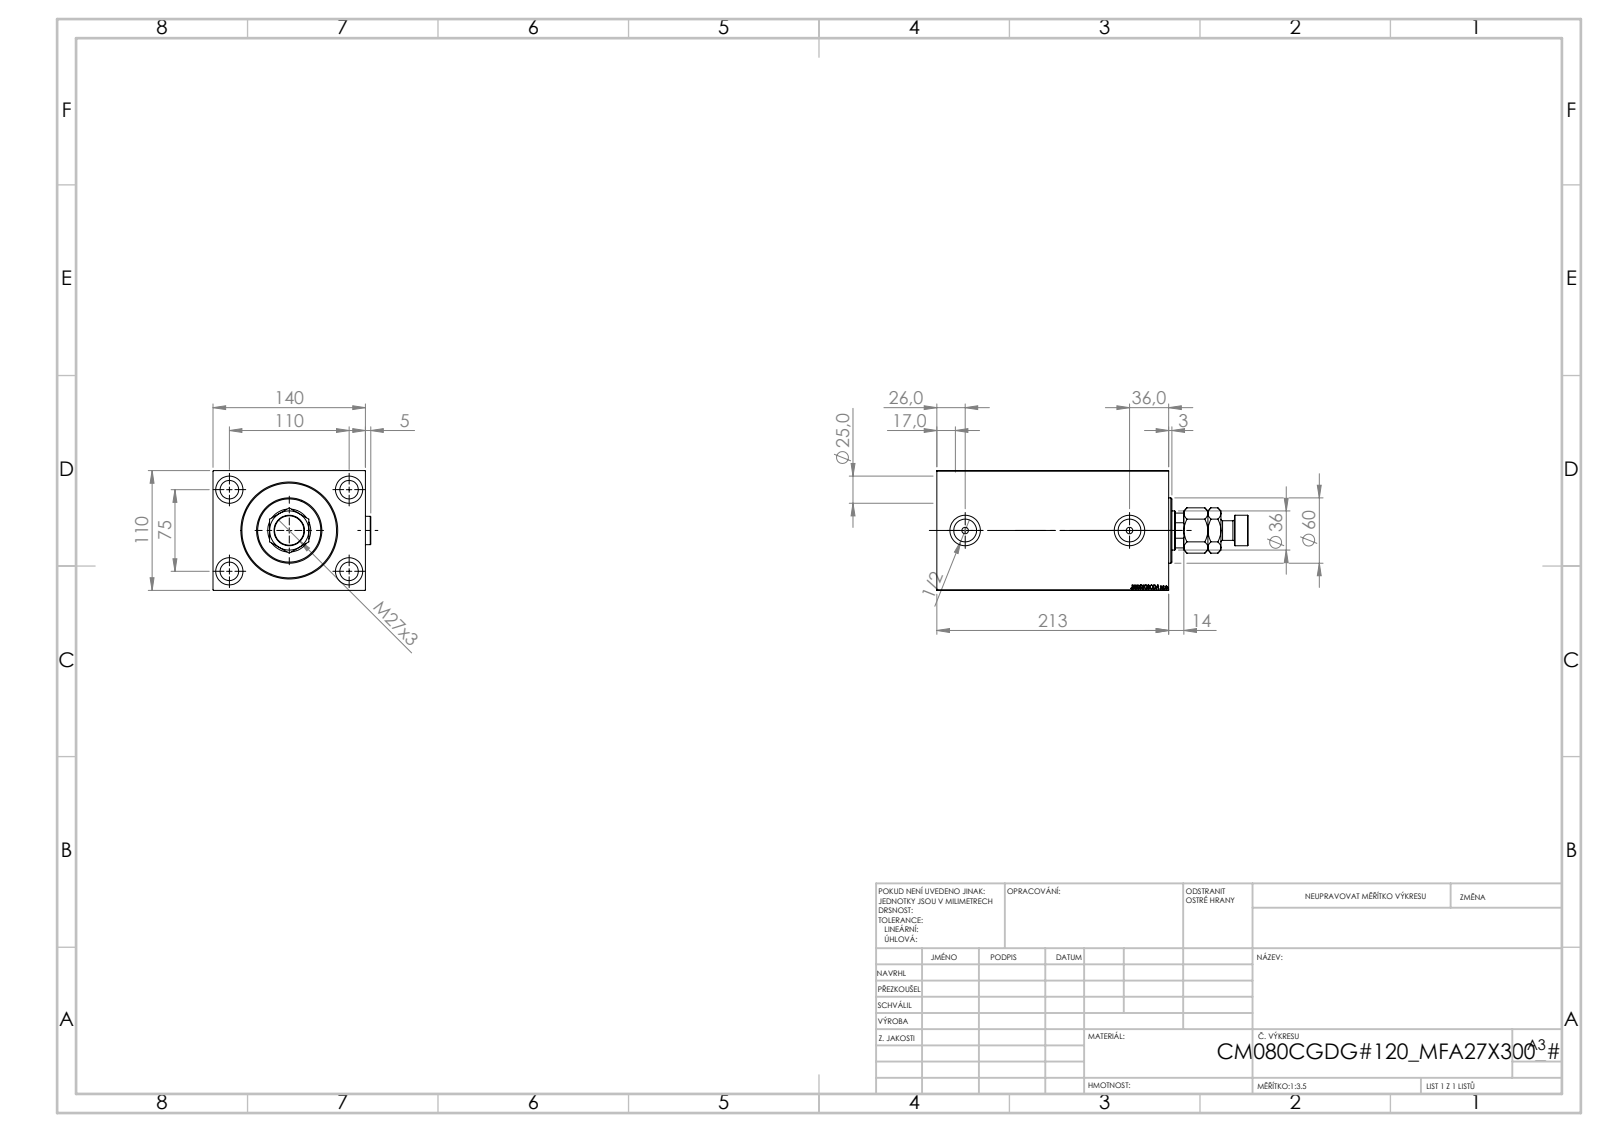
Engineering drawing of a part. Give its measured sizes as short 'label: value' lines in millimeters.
name: V450CM_VC_B; V450CM_C_VCP; V450CM_C_Body; MFA (+1 more)
written by: SolidWorks 2019 (CONFIG_CONTROL_DESIGN)
unit: mm
bodies: 6 solids, 971 faces (459 planar, 82 cylindrical, 430 other)
size: 286 × 144.9 × 110
volume: 2 604 000 mm³; area: 308 790 mm²
holes: 4× ⌀17, 4× ⌀25, 2× ⌀6, 2× ⌀20.96, 2× ⌀28, 1× ⌀25.5, 1× ⌀36, 1× ⌀39.5, 1× ⌀80, 1× ⌀82, 1× ⌀87
bosses: 2× ⌀26, 1× ⌀60, 1× ⌀28, 1× ⌀18
rounds: 1× R17.5
face distances: 110, 140, 213, 192, 21, 14, 199, 178, 134, 120
hole spacings: 66.57, 75, 110, 133.14, 151
